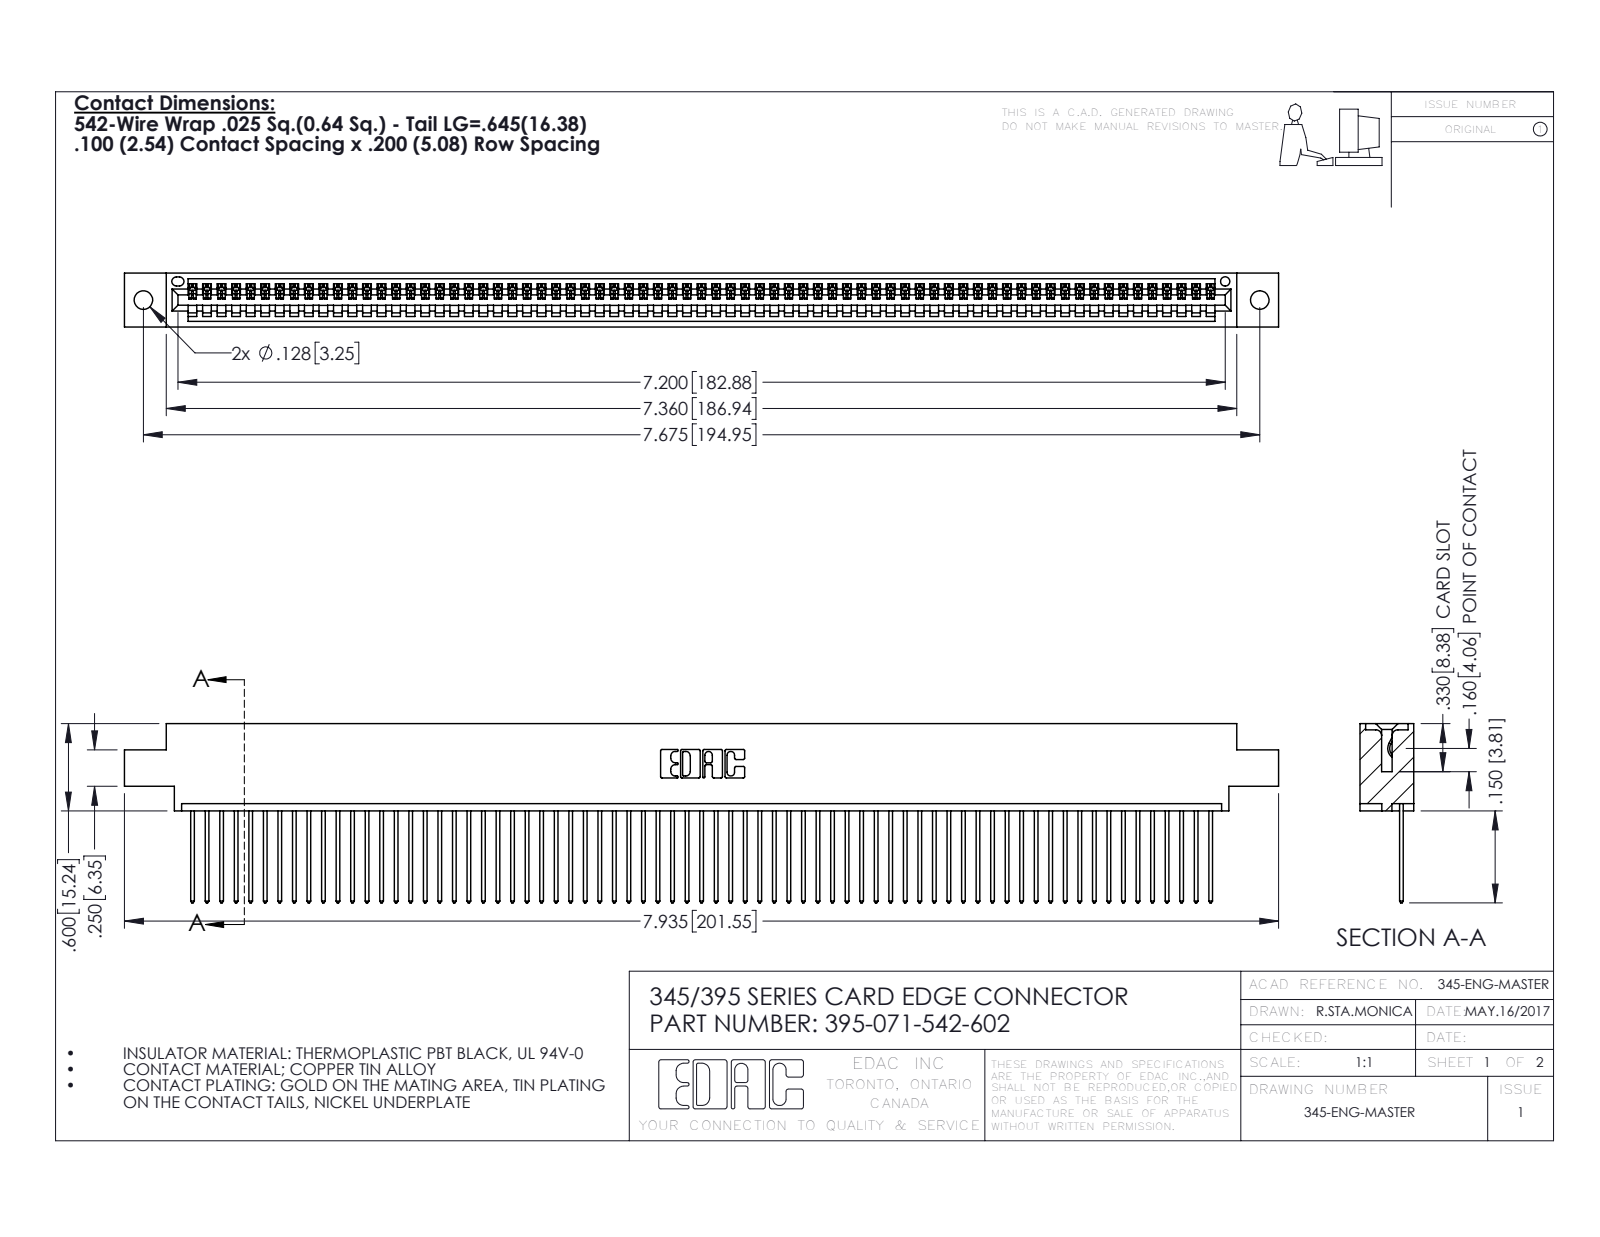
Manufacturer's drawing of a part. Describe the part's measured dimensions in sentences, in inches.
The part is named "345 Part_0.170 Offset - 0.128 Dia; 345-292-001_345-293-142; 395-071-542-602". Its 3-D file was written by "SolidWorks 2016 (CONFIG_CONTROL_DESIGN)". It is 72 solids with 4248 faces: 2924 planar, 1324 cylindrical and 0 other. Overall it measures 7.935 by 1.232 by 0.37 inches. Its volume is 1.183 cubic inches and its surface area 41.87 square inches. Round holes: 2 of diameter 0.128, 1 of diameter 0.064. Partial cylindrical surfaces (rounded edges, fillets, slot ends): 142 of radius 0.006, 142 of radius 0.01, 22 of radius 0.01, 6 of radius 0.007, 6 of radius 0.031, 3 of radius 0.026, 2 of radius 0.031, 2 of radius 0.04. The main face-to-face distances are 0.072, 0.298, 0.37, 0.098, 0.272, 0.025, 0.2, 0.225, 0.175, 0.149. The hole center spacings are 0.27, 7.439, 7.675.
